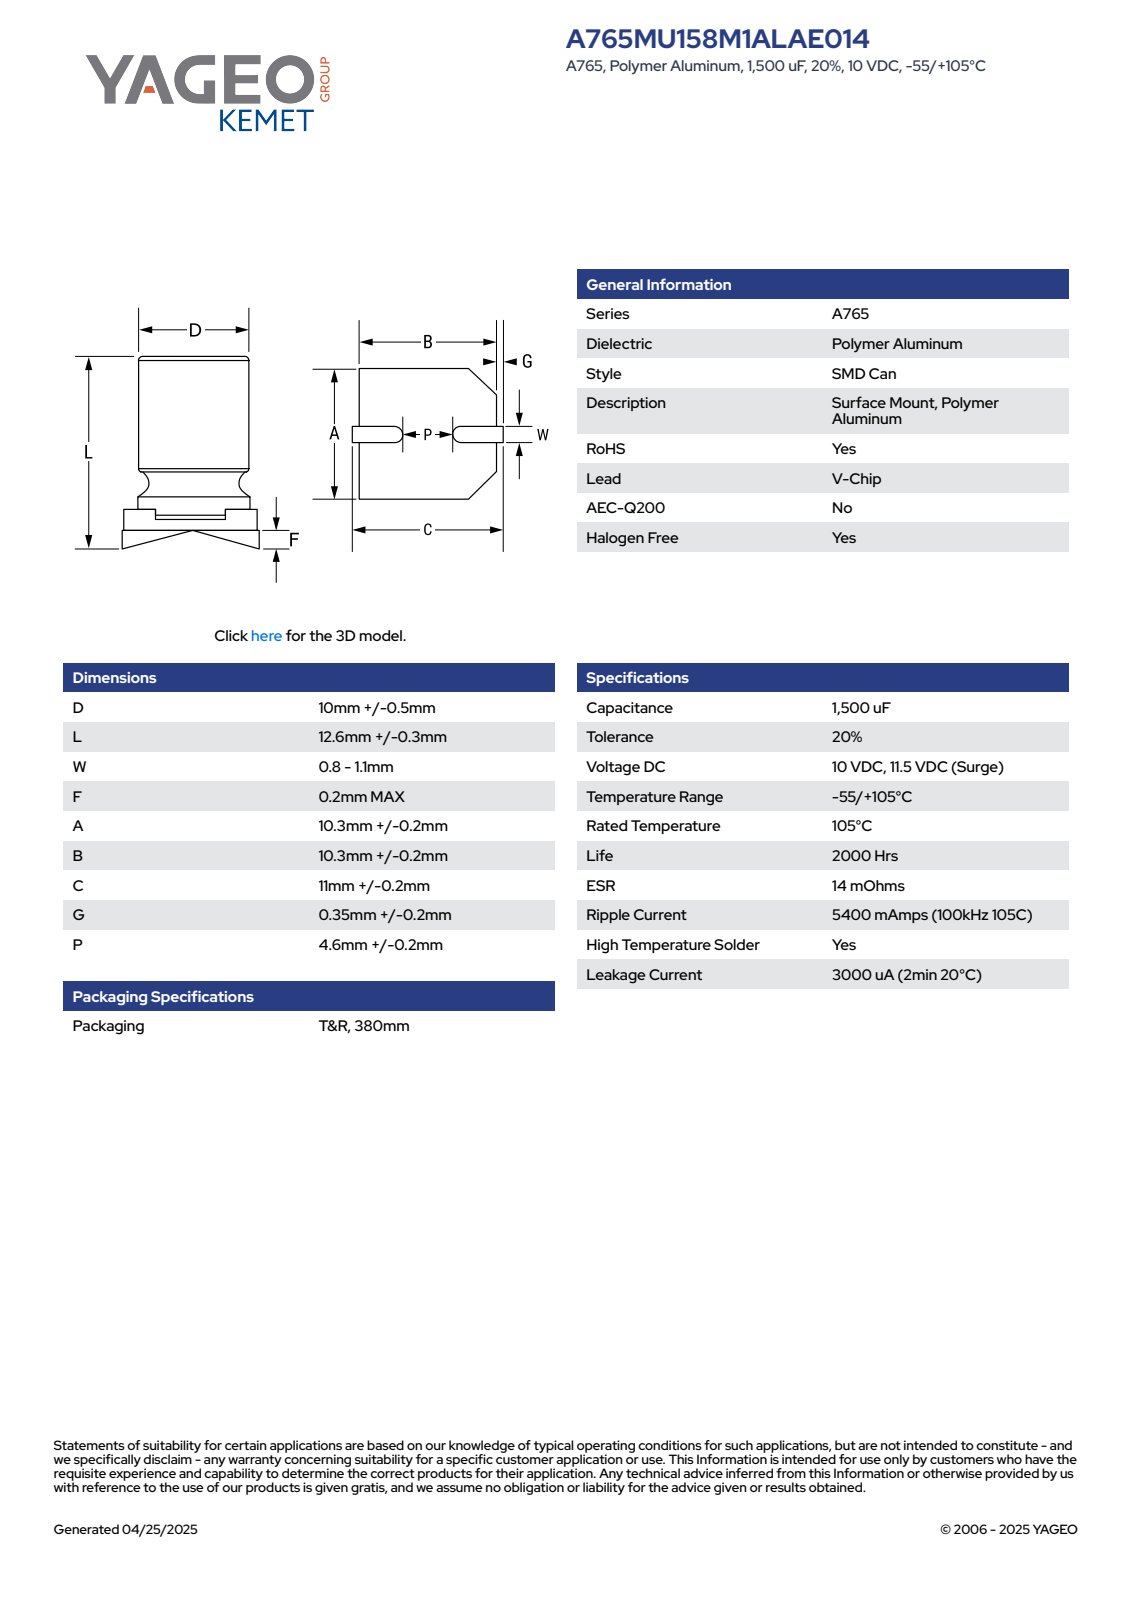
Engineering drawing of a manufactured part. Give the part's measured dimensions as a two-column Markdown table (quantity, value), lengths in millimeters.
| quantity | value |
| --- | --- |
| part name | CAC_KS_10X12.6_D10.5L12.9W1.1F0.2A10.5B10.5C11.2P4.8 |
| STEP written by | SolidWorks 2014 (AUTOMOTIVE_DESIGN) |
| units | millimeters |
| bodies | 5 solids, 76 faces (59 planar, 11 cylindrical, 6 other) |
| overall size | 12.9 × 11.2 × 10.5 |
| volume | 1 044 mm³ |
| surface area | 888 mm² |
| round bosses / shafts (diameter × count) | 10.04 × 1 |
| partial cylindrical surfaces (radius × count) | 0.2 × 2, 4.17 × 1, 5.25 × 1 |
| main face-to-face distances | 0.64, 12.7, 12.06, 12.71, 12.07, 10.5, 2.59, 3.23, 9.47, 9.48 |
